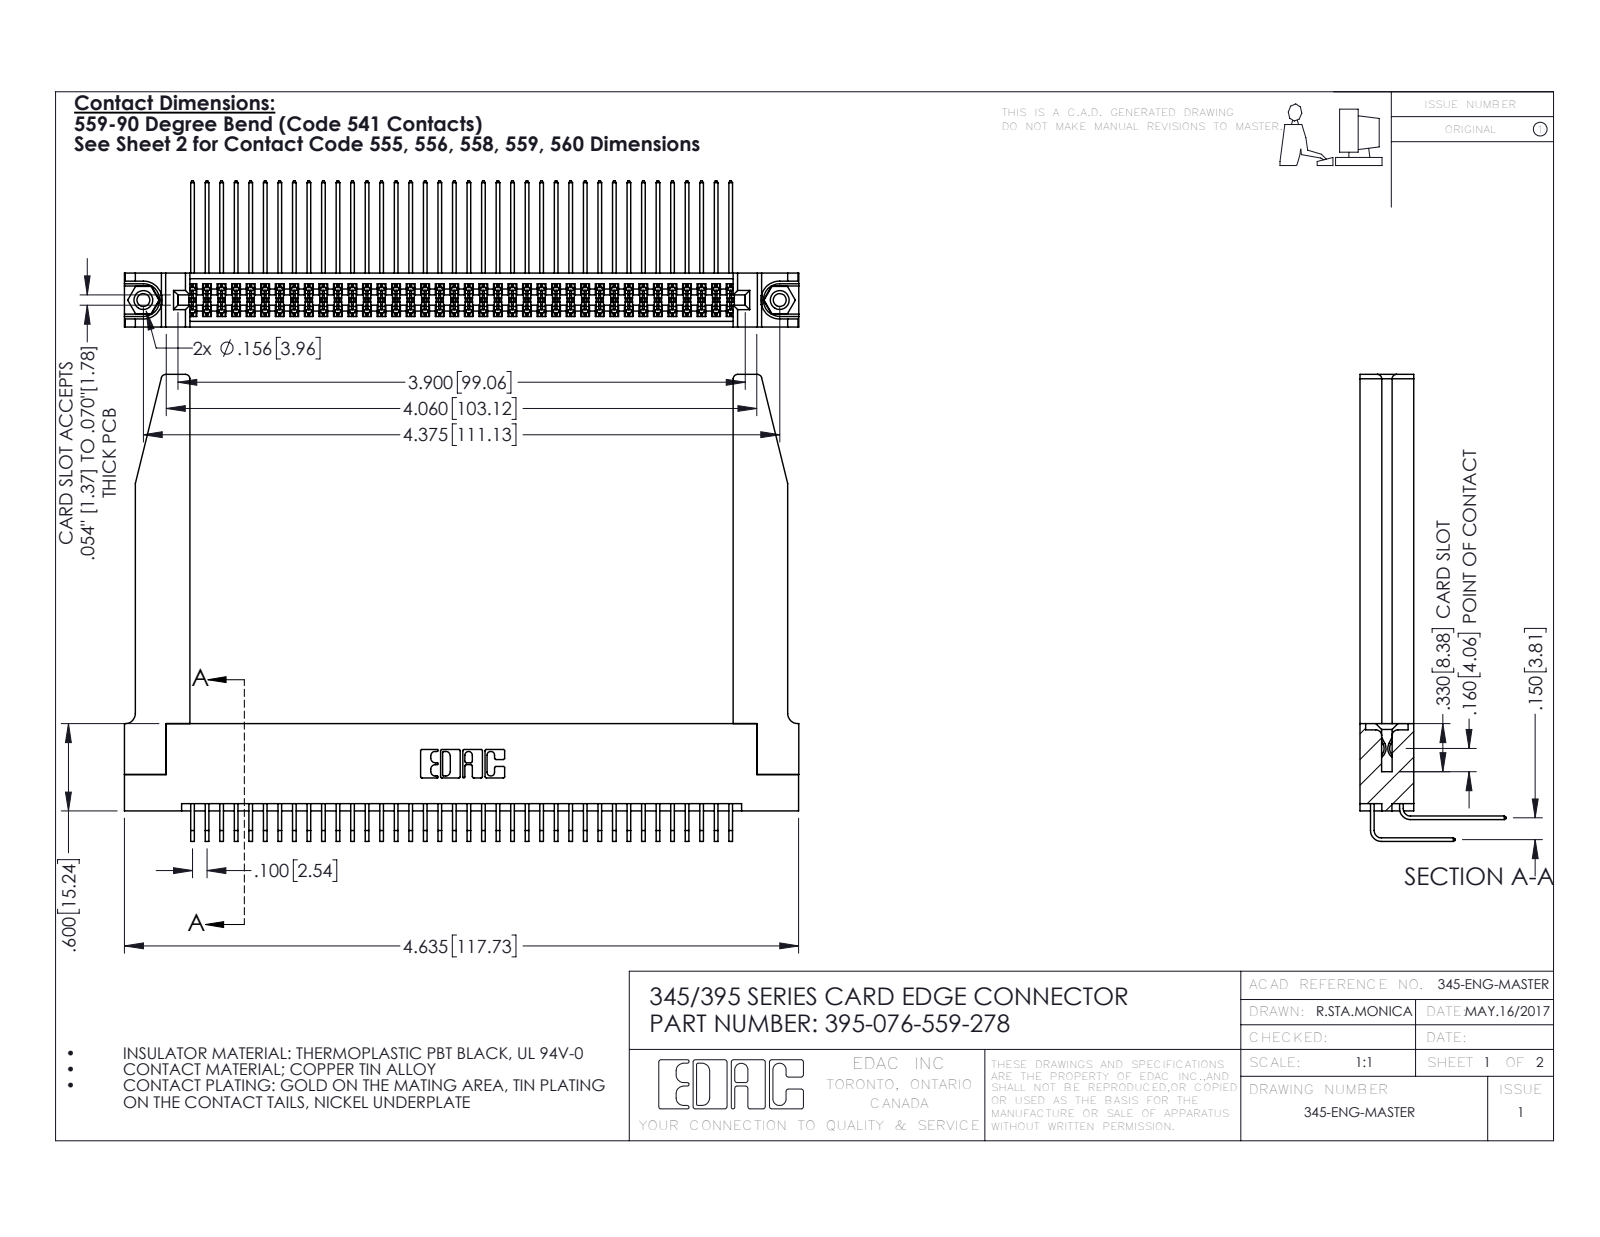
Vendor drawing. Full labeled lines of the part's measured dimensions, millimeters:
Part name (STEP PRODUCT): 345 Part_Flush Mounting Lugs - 0.156 Dia-TH; 345-220-078_345-220-078; 345-292-001_558 559 Tail - 1; 345-292-001_559 Tail - 2 (+2 more)
STEP written by: SolidWorks 2016 (CONFIG_CONTROL_DESIGN)
Units: millimetres
Bodies: 81 solids, 4312 faces (2882 planar, 1378 cylindrical, 52 other)
Overall size (bounding box): 117.8 × 81.5 × 25.5
Volume: 19 620 mm³ · Surface area: 26 320 mm²
Round holes (diameter × count): ⌀2.3 ×2, ⌀3.2 ×2, ⌀4 ×2, ⌀1.6 ×1
Round bosses / shafts (diameter × count): ⌀3.9 ×2
Partial cylindrical surfaces — rounded edges, fillets, slot ends (radius × count): R0.2 ×114, R0.3 ×22, R0.8 ×8, R0.2 ×6, R0.8 ×6, R0.7 ×3, R0.4 ×2, R0.5 ×2
Main face-to-face distances: 9.4, 1.8, 7.6, 5.1, 2.5, 6.9, 0.6, 5.7, 4.4, 3.8
Hole centre spacings: 6.9, 105.1, 111.1
